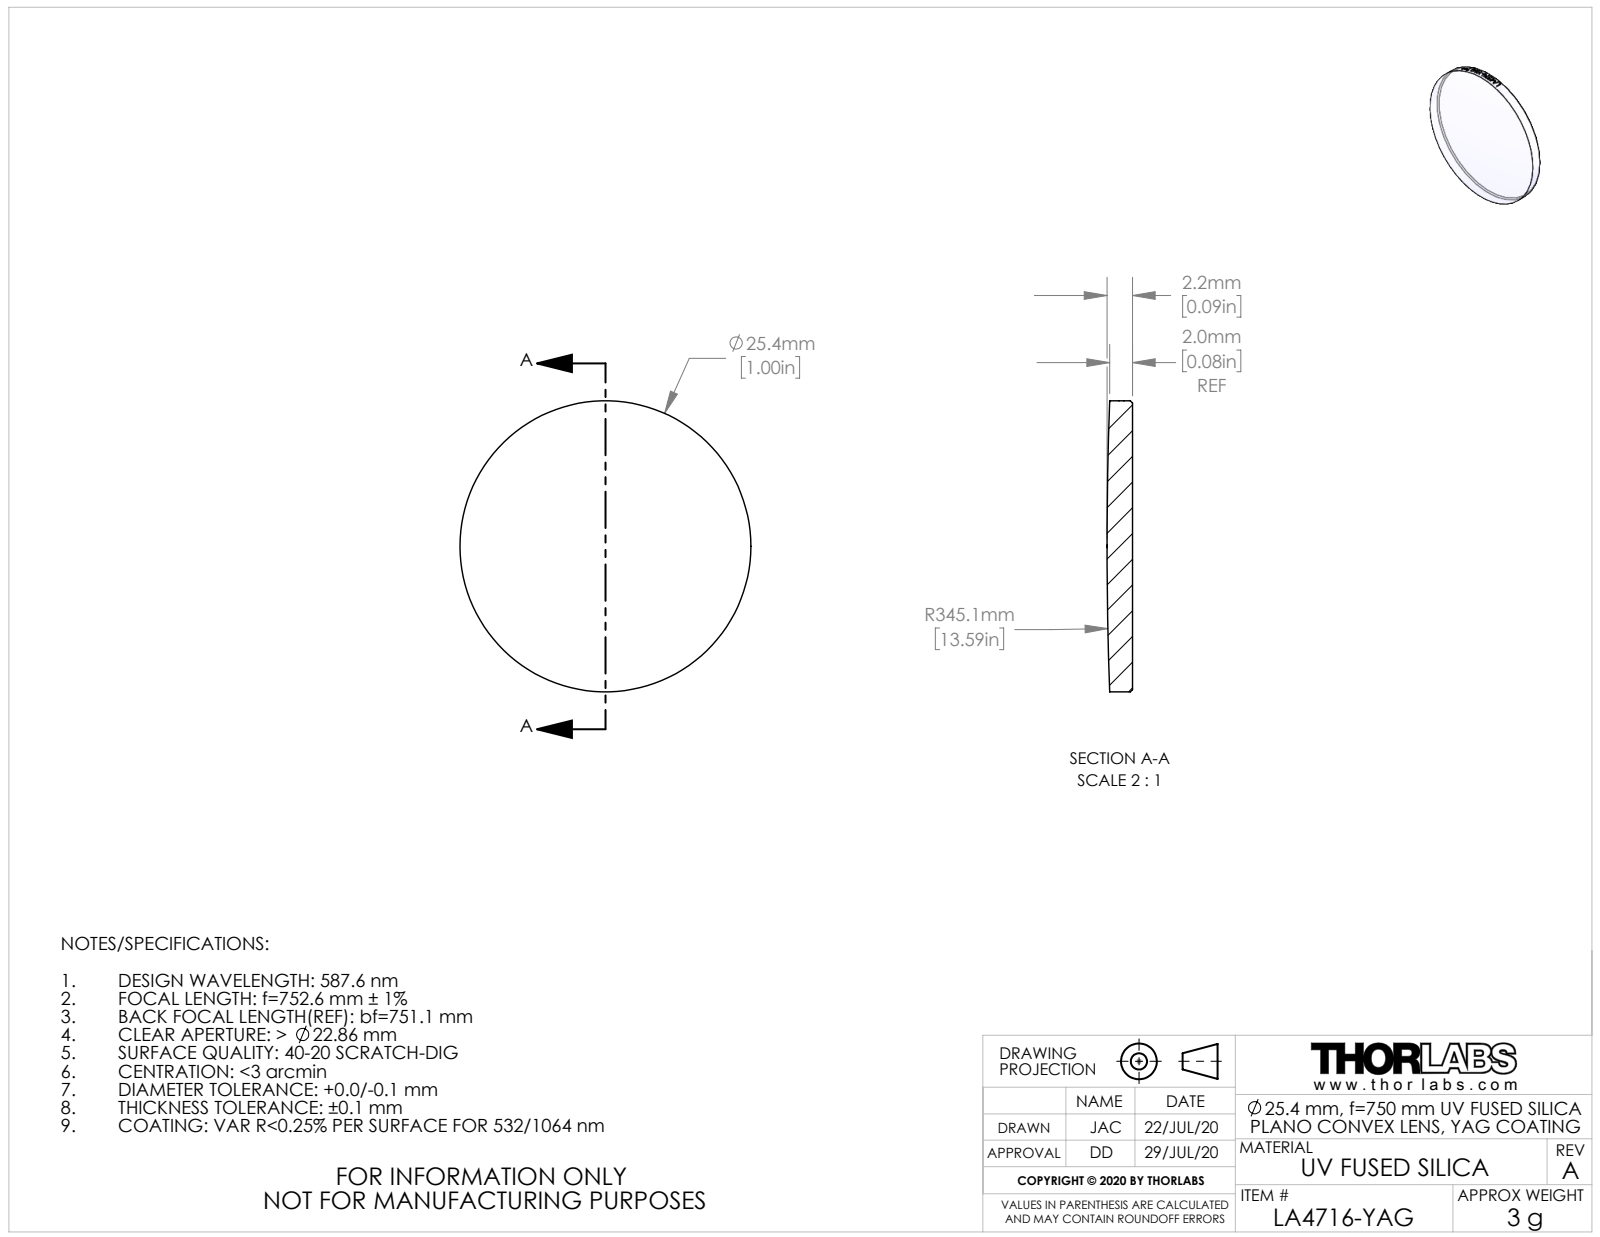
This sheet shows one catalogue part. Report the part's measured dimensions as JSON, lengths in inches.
{"part_name": "TTN217854-E0W", "step_written_by": "SolidWorks 2018 (CONFIG_CONTROL_DESIGN)", "units": "inches", "bodies": {"solids": 1, "faces": 25, "planar": 1, "cylindrical": 20, "other": 4}, "overall_size": [1, 1, 0.088], "volume_in3": 0.065, "surface_area_in2": 1.804, "round_bosses_or_shafts": [[1, 1]]}
